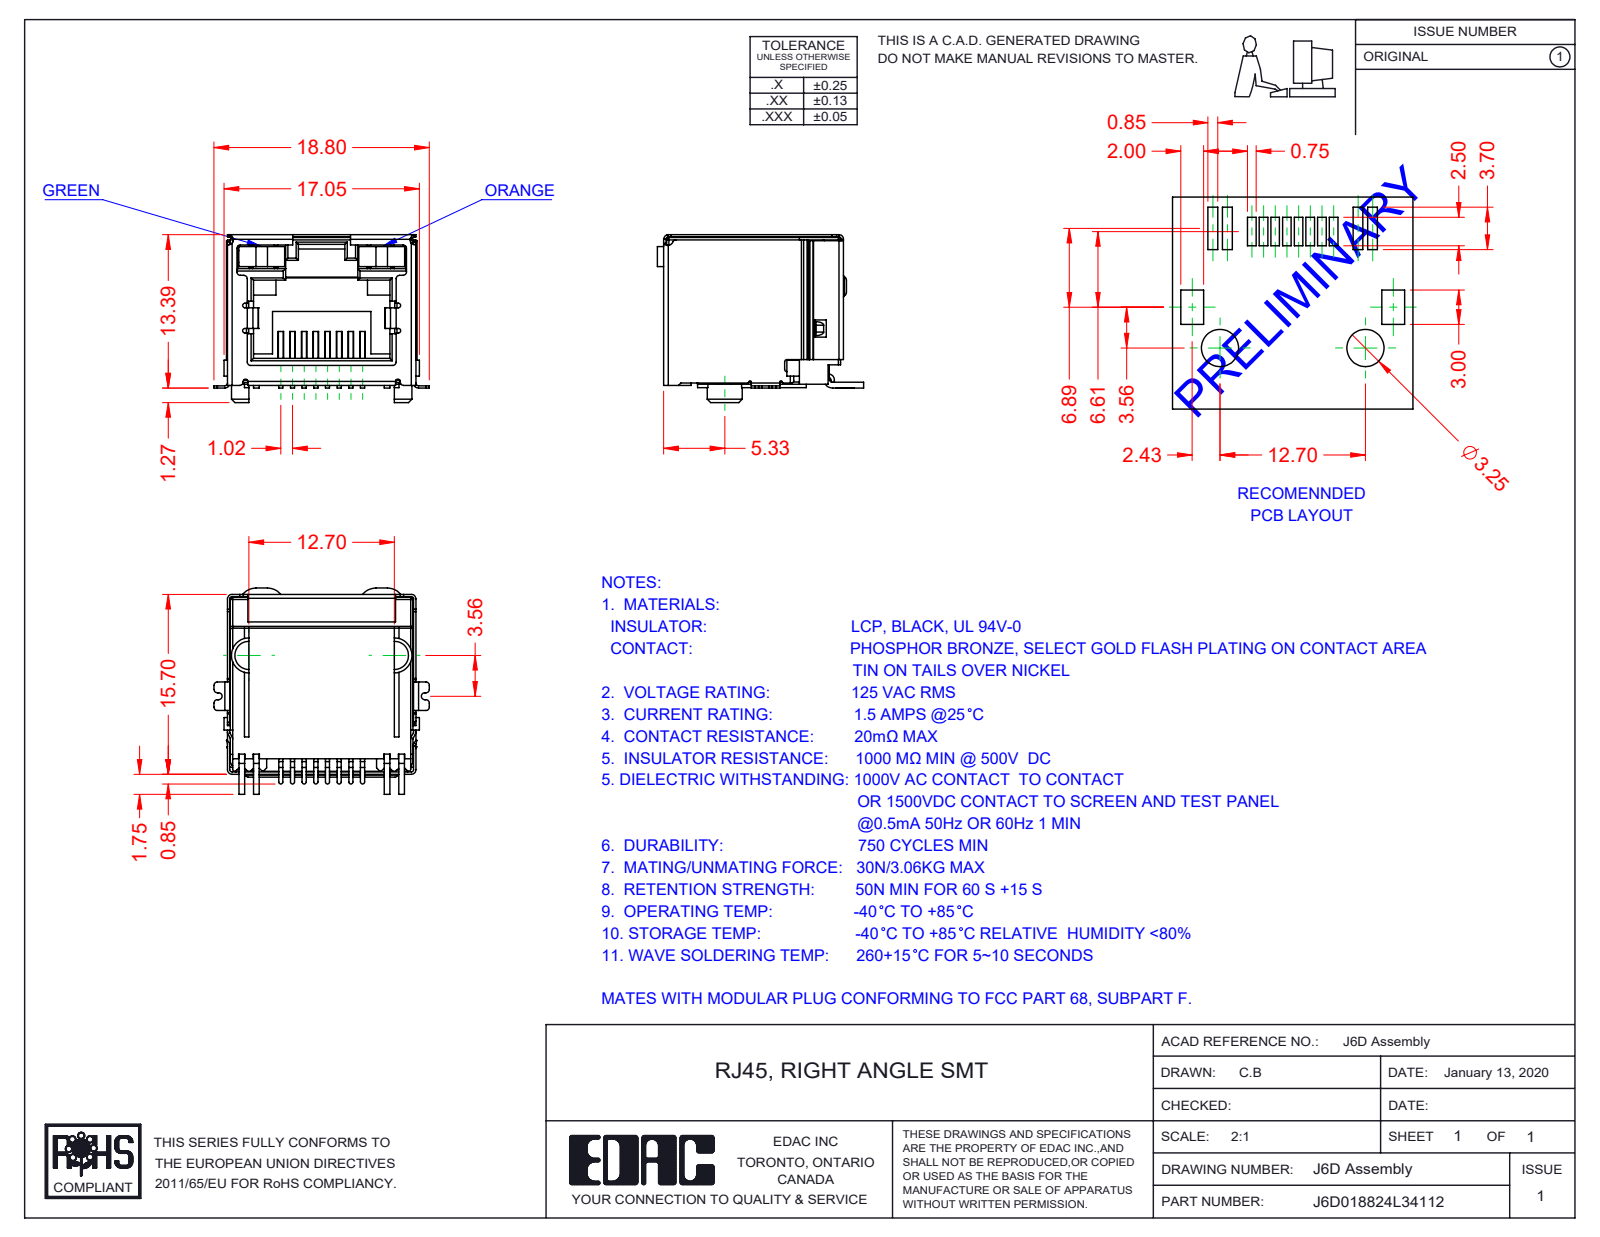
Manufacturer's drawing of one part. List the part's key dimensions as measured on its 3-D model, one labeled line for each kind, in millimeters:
Part name (STEP PRODUCT): J6D018824L34112; 6D LED RH_4-Orange; 6D Insulator; 6D LED LH_3-Green (+2 more)
STEP written by: SolidWorks 2016 (CONFIG_CONTROL_DESIGN)
Units: millimetres
Bodies: 12 solids, 893 faces (644 planar, 216 cylindrical, 33 other)
Overall size (bounding box): 18.8 × 18 × 14.65
Volume: 1 804 mm³ · Surface area: 4 898 mm²
Partial cylindrical surfaces — rounded edges, fillets, slot ends (radius × count): R0.3 ×39, R0.2 ×37, R0.4 ×16, R0.1 ×12, R0.15 ×8, R0.18 ×8, R0.5 ×6, R1.5 ×5
Main face-to-face distances: 16, 16.25, 16.2, 2.25, 1, 15.95, 16.05, 12.8, 0.45, 16.45
